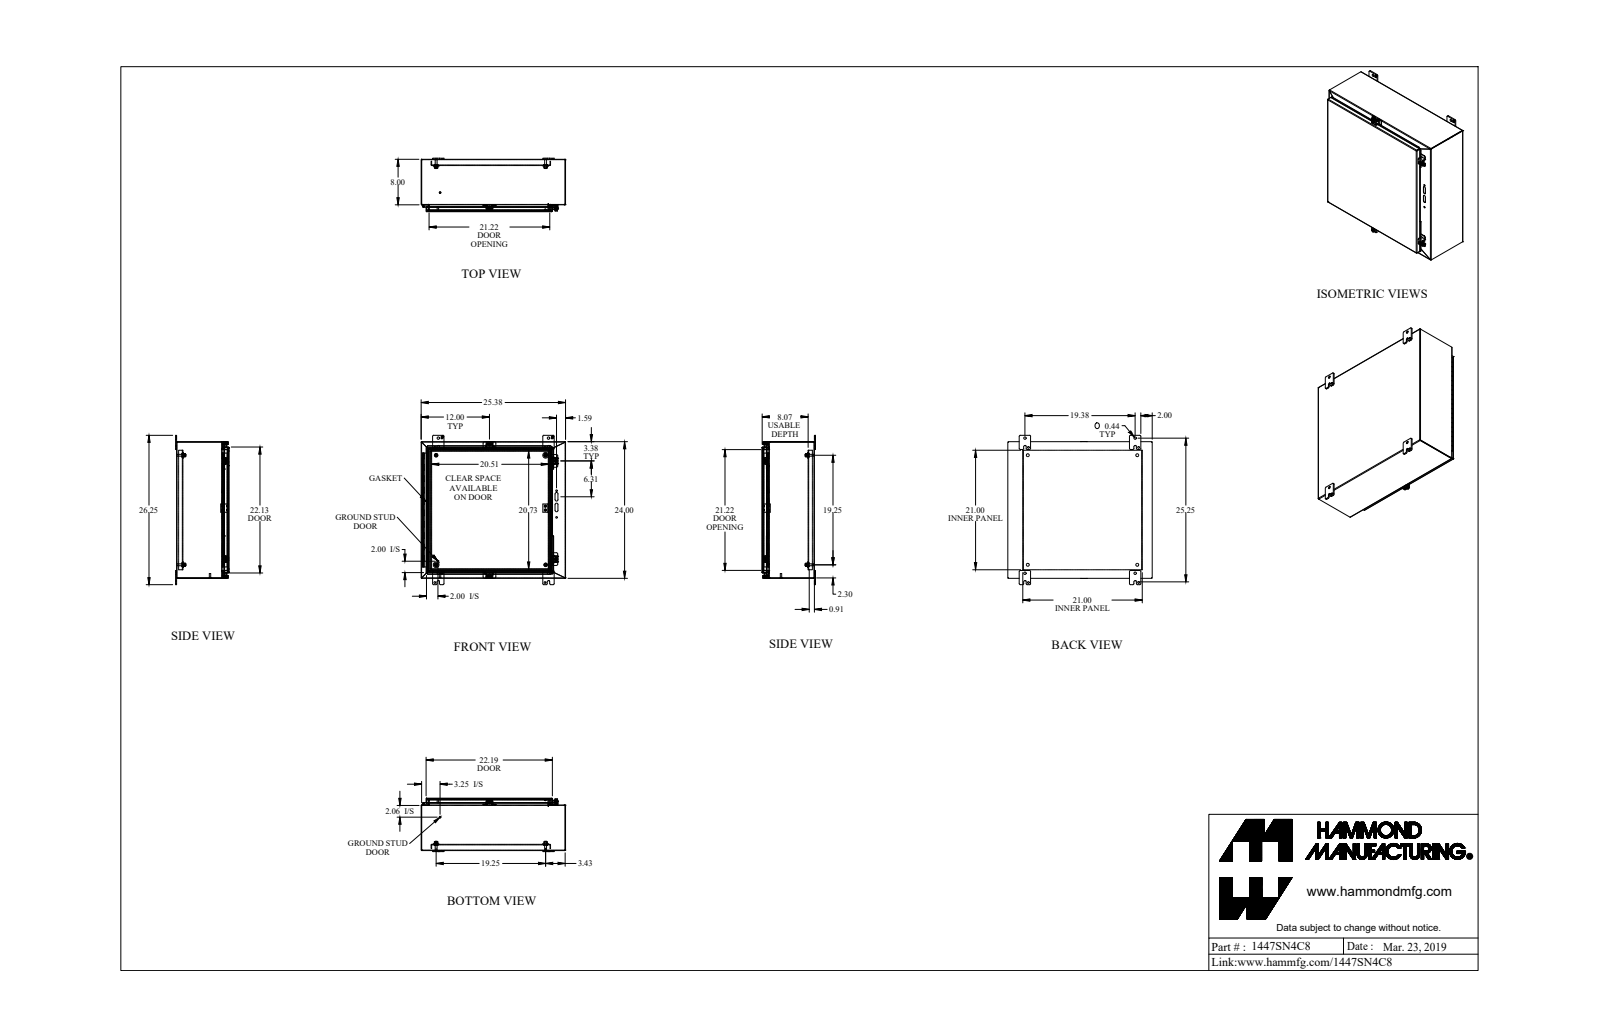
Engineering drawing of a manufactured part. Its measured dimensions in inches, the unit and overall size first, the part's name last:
Units: inches
Overall size (bounding box): 26.25 × 25.375 × 9.397
Round holes (diameter × count): ⌀0.313 ×6, ⌀0.213 ×4, ⌀0.265 ×4, ⌀0.375 ×4, ⌀0.437 ×4, ⌀0.5 ×4, ⌀0.15 ×2, ⌀0.156 ×2, ⌀0.281 ×2, ⌀0.307 ×2, ⌀0.445 ×2, ⌀0.187 ×1
Round bosses / shafts (diameter × count): ⌀0.65 ×4, ⌀0.5 ×4, ⌀0.39 ×4, ⌀0.375 ×4, ⌀0.33 ×4, ⌀0.25 ×4, ⌀0.244 ×4, ⌀1 ×2
Partial cylindrical surfaces — rounded edges, fillets, slot ends (radius × count): R0.188 ×24, R0.25 ×24, R0.036 ×23, R0.108 ×23, R0.048 ×21, R0.143 ×21, R0.045 ×10, R0.125 ×8
Main face-to-face distances: 0.072, 9.066, 9.138, 0.072, 9.138, 9.21, 0.095, 8.106, 8.034, 1.032
Hole centre spacings: 19.25, 21.146, 2.122, 19.375, 1.735, 9.612, 12.155, 18.346
Volume: 220.4 in³ · Surface area: 5 775 in²
Bodies: 42 solids, 1450 faces (860 planar, 497 cylindrical, 93 other)
Part name (STEP PRODUCT): 1447SN4C8_Default
STEP written by: SolidWorks 2019 (CONFIG_CONTROL_DESIGN)
